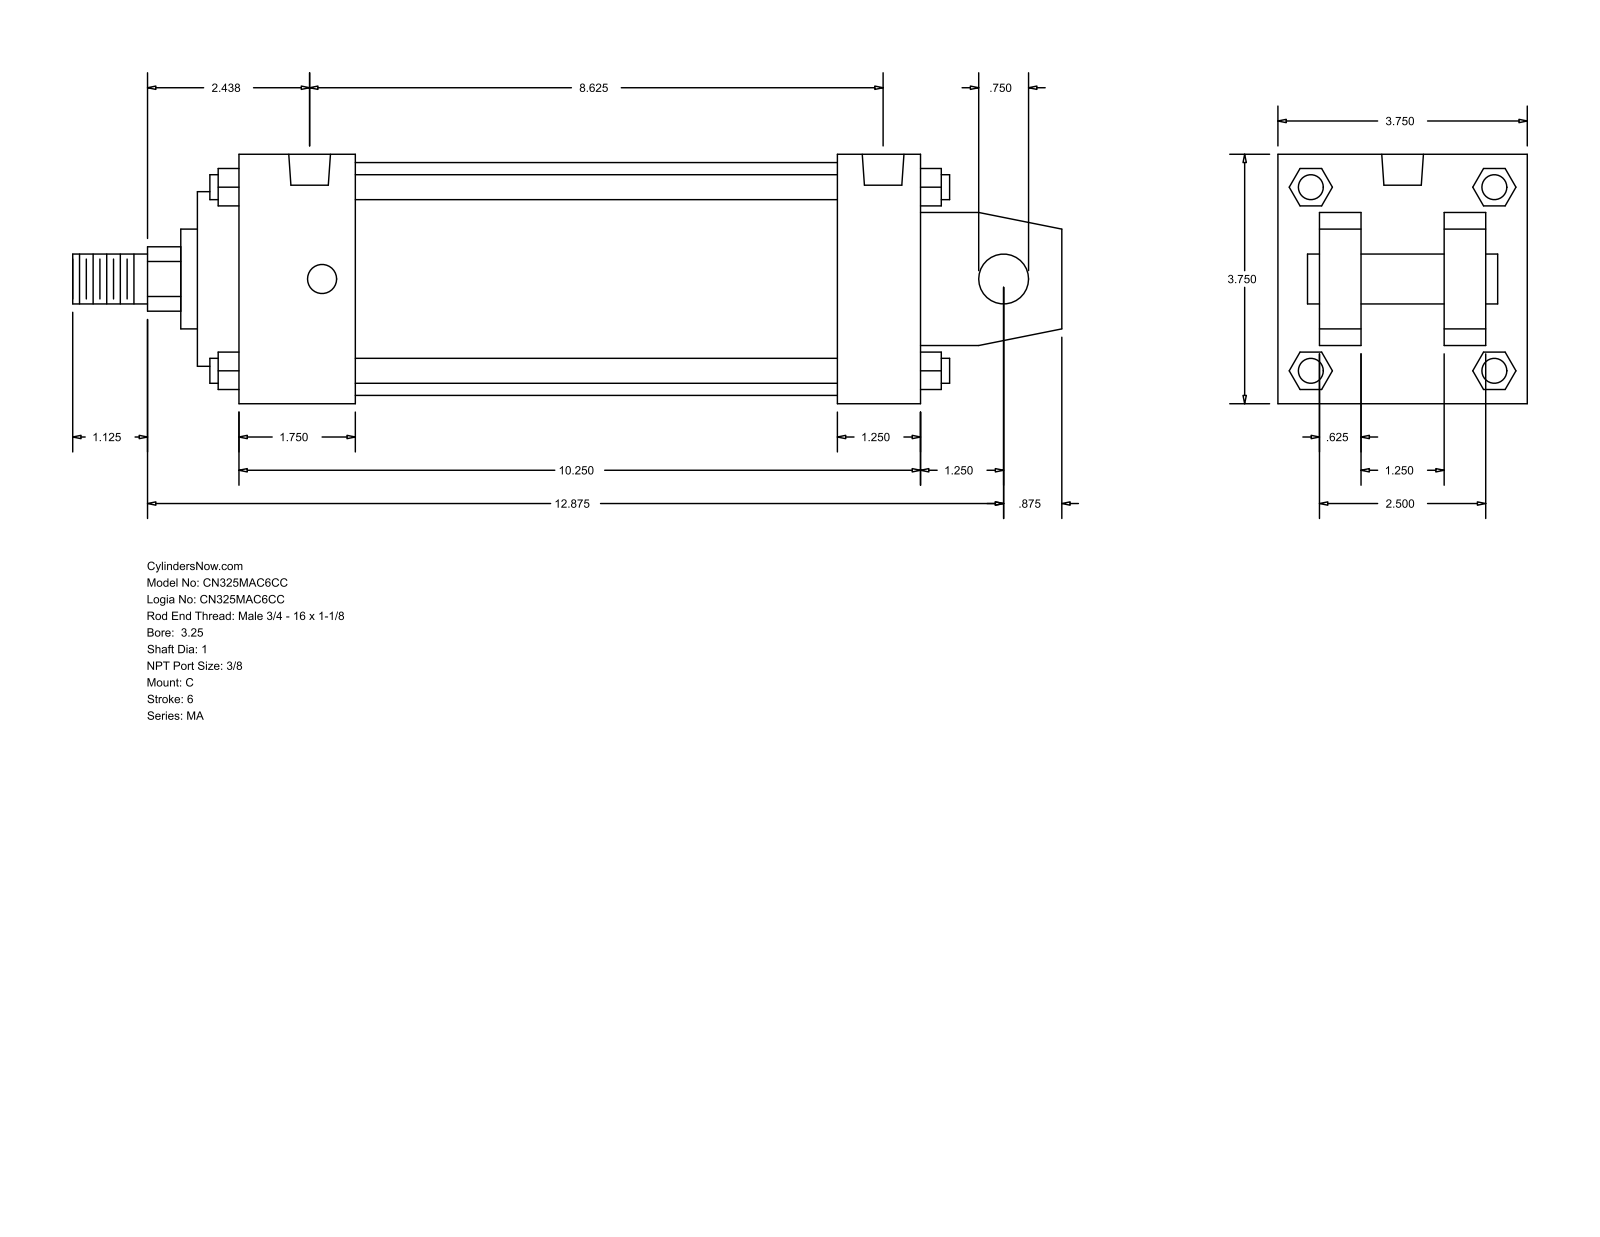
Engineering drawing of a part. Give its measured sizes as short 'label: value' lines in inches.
name: MA_C__0325_1
written by: GSSL Pune (CONFIG_CONTROL_DESIGN)
unit: in
bodies: 0 solids, 141 faces (109 planar, 32 cylindrical, 0 other)
size: 14.875 × 3.75 × 3.75
holes: 4× ⌀0.437, 2× ⌀0.627
bosses: 4× ⌀0.375, 2× ⌀0.75, 1× ⌀3.5, 1× ⌀2.625, 1× ⌀1.5, 1× ⌀1
rounds: 1× R0.484
face distances: 3.75, 0.625, 2.5, 10.25, 1.25, 3.125, 1.875, 10.875, 9, 1.25
hole spacings: 0.187, 8.25, 8.438, 8.625
